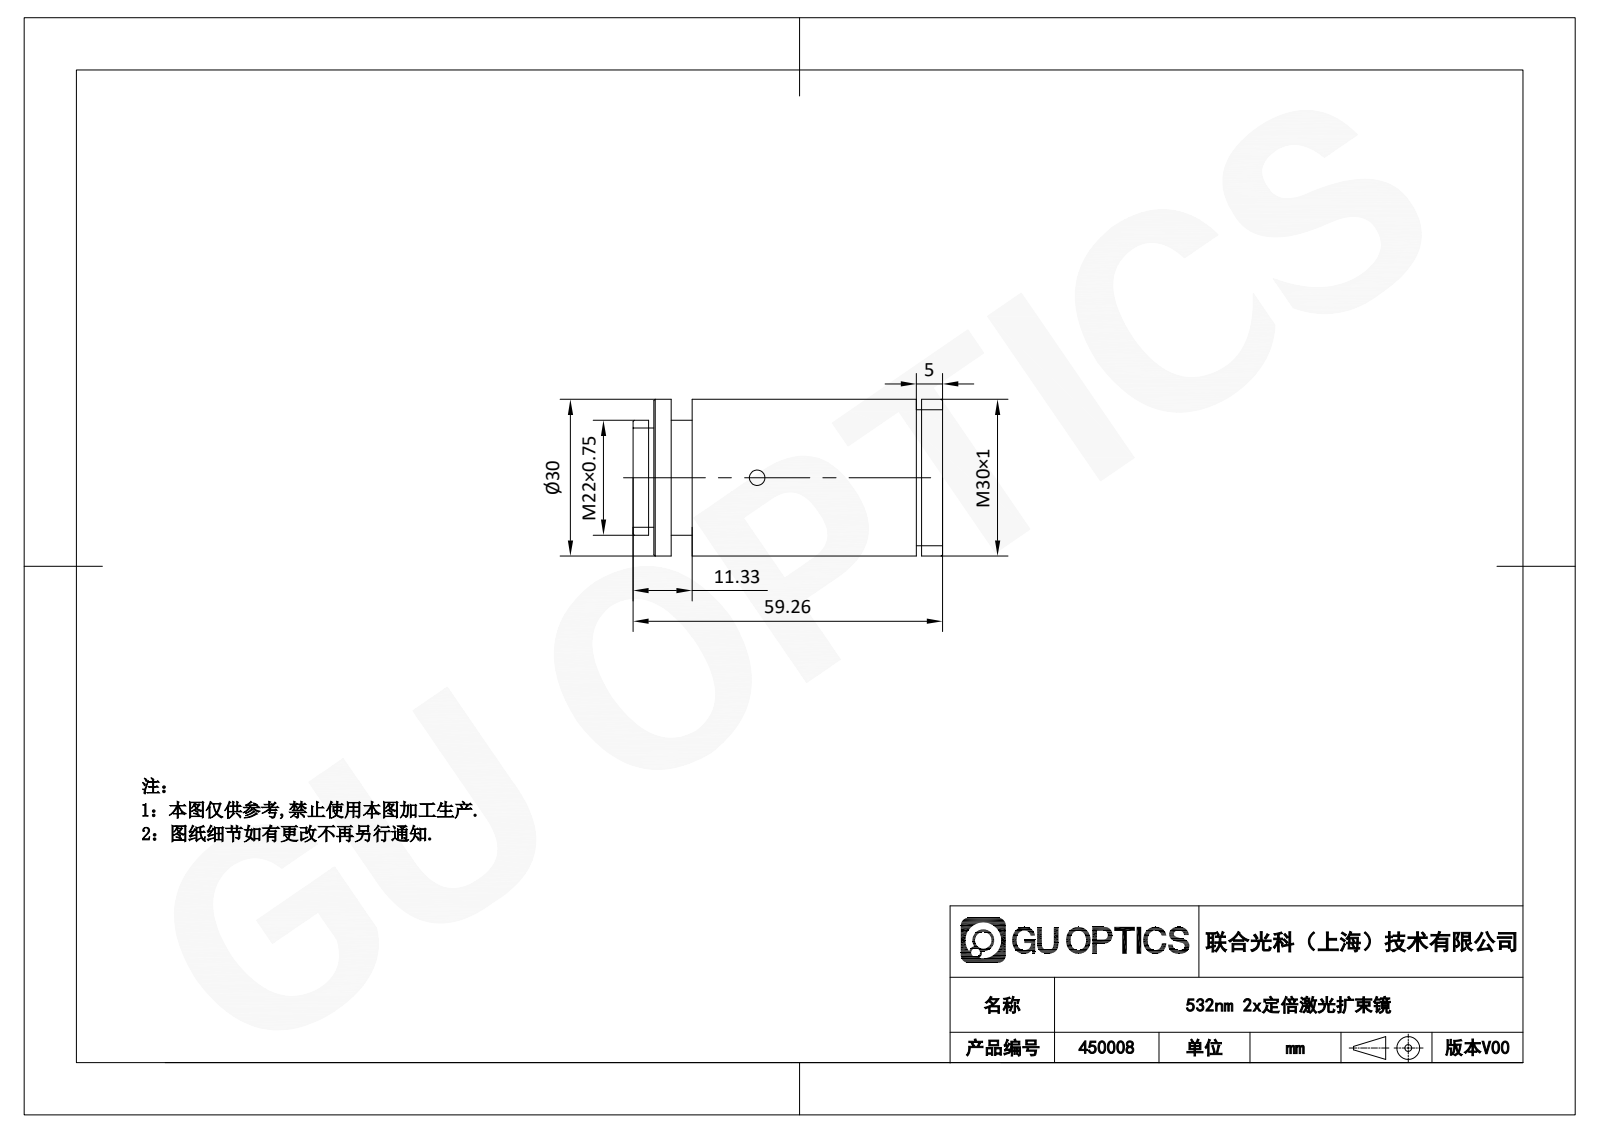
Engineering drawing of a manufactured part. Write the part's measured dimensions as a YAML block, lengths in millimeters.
part_name: "450008"
step_written_by: "SolidWorks 2020 (AUTOMOTIVE_DESIGN)"
units: millimeters
bodies: {solids: 1, faces: 43, planar: 11, cylindrical: 22, other: 10}
overall_size: [59.26, 30, 30]
volume: 31793
surface_area: 10589
round_holes:
  - {diameter: 8, count: 1}
  - {diameter: 18, count: 1}
round_bosses_or_shafts:
  - {diameter: 30, count: 1}
  - {diameter: 26, count: 1}
  - {diameter: 22, count: 1}
  - {diameter: 19, count: 1}
face_to_face_distances: [4, 55.26, 47.93, 7.33, 51.26, 3.33, 51.93, 43.93, 1, 11.33]
